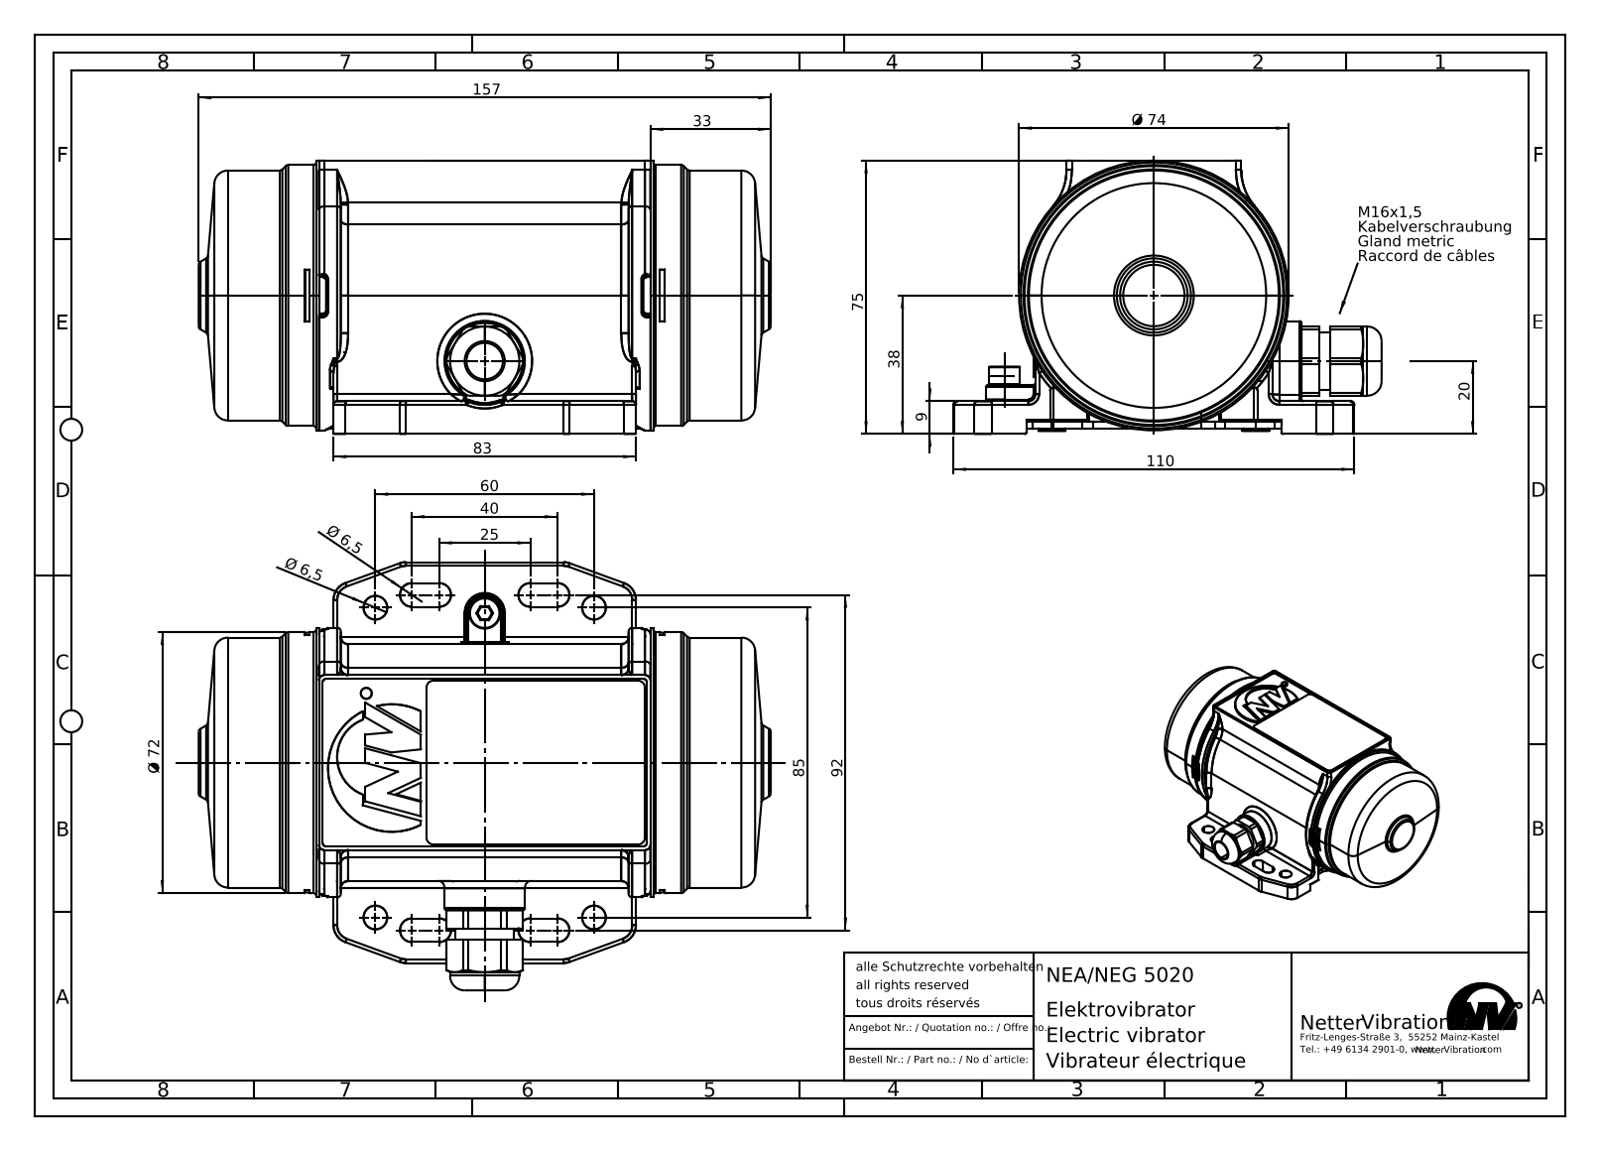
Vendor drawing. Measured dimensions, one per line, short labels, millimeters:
name: NEA-NEG 5020
written by: SolidWorks 2015 (AUTOMOTIVE_DESIGN)
unit: mm
bodies: 0 solids, 1664 faces (858 planar, 424 cylindrical, 382 other)
size: 157 × 117.5 × 75.01
holes: 4× ⌀4.5, 1× ⌀10, 1× ⌀70
bosses: 5× ⌀4, 4× ⌀7.5, 1× ⌀74, 1× ⌀71.6, 1× ⌀68.6, 1× ⌀67, 1× ⌀60, 1× ⌀53.5
rounds: 60× R0.2, 40× R1, 36× R0.5, 22× R2, 16× R0.3, 13× R5, 8× R1.5, 4× R5.25
face distances: 2, 73.5, 71.5, 0.75, 72.75, 70.75, 0.55, 73.3, 71.3, 5.5
hole spacings: 56, 60, 82.07
